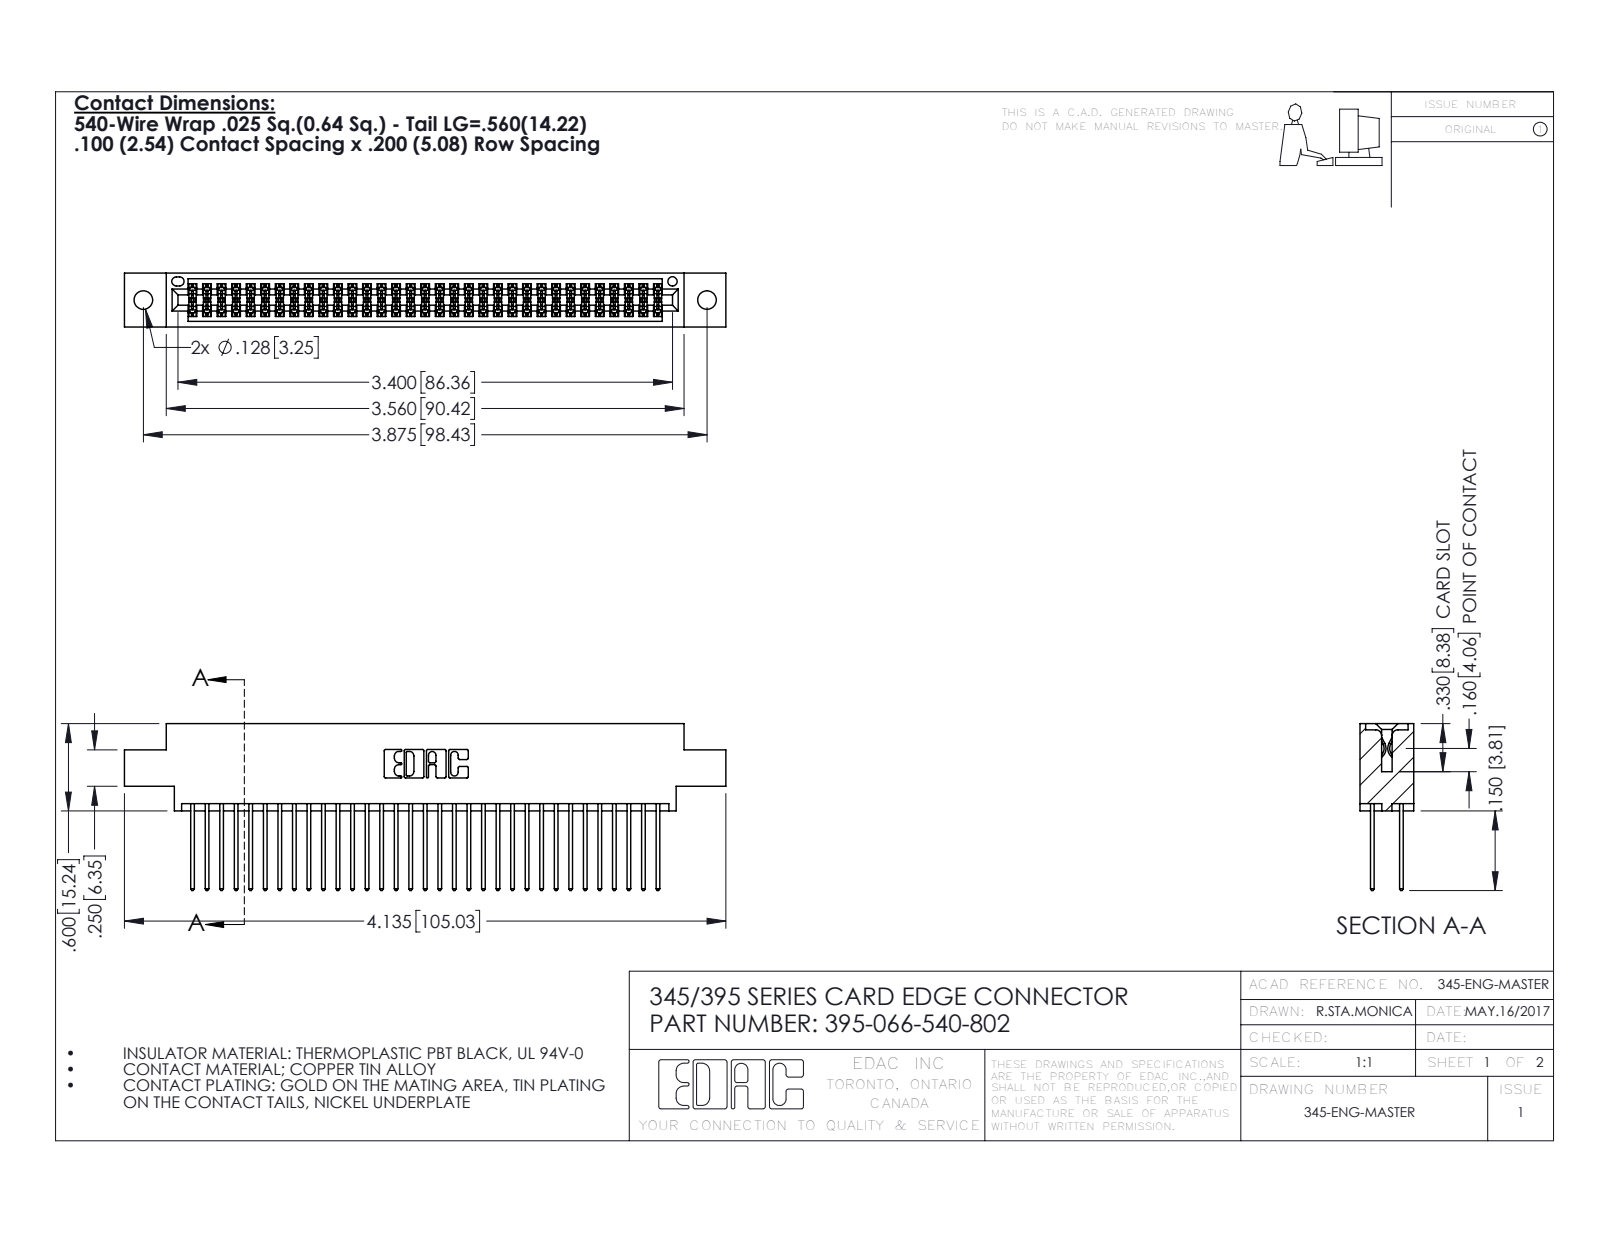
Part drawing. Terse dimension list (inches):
name: 345 Part_0.170 Offset - 0.128 Dia; 345-292-001_345-293-140; 395-066-540-802
written by: SolidWorks 2016 (CONFIG_CONTROL_DESIGN)
unit: in
bodies: 67 solids, 3430 faces (2262 planar, 1168 cylindrical, 0 other)
size: 4.135 × 1.147 × 0.37
volume: 0.624 in³; area: 24.74 in²
holes: 2× ⌀0.128, 1× ⌀0.064
rounds: 99× R0.006, 66× R0.01, 22× R0.01, 6× R0.007, 6× R0.031, 3× R0.026, 2× R0.014, 2× R0.019
face distances: 0.298, 0.072, 0.2, 0.098, 0.272, 0.025, 0.37, 0.225, 0.175, 0.149
hole spacings: 0.27, 3.64, 3.875
